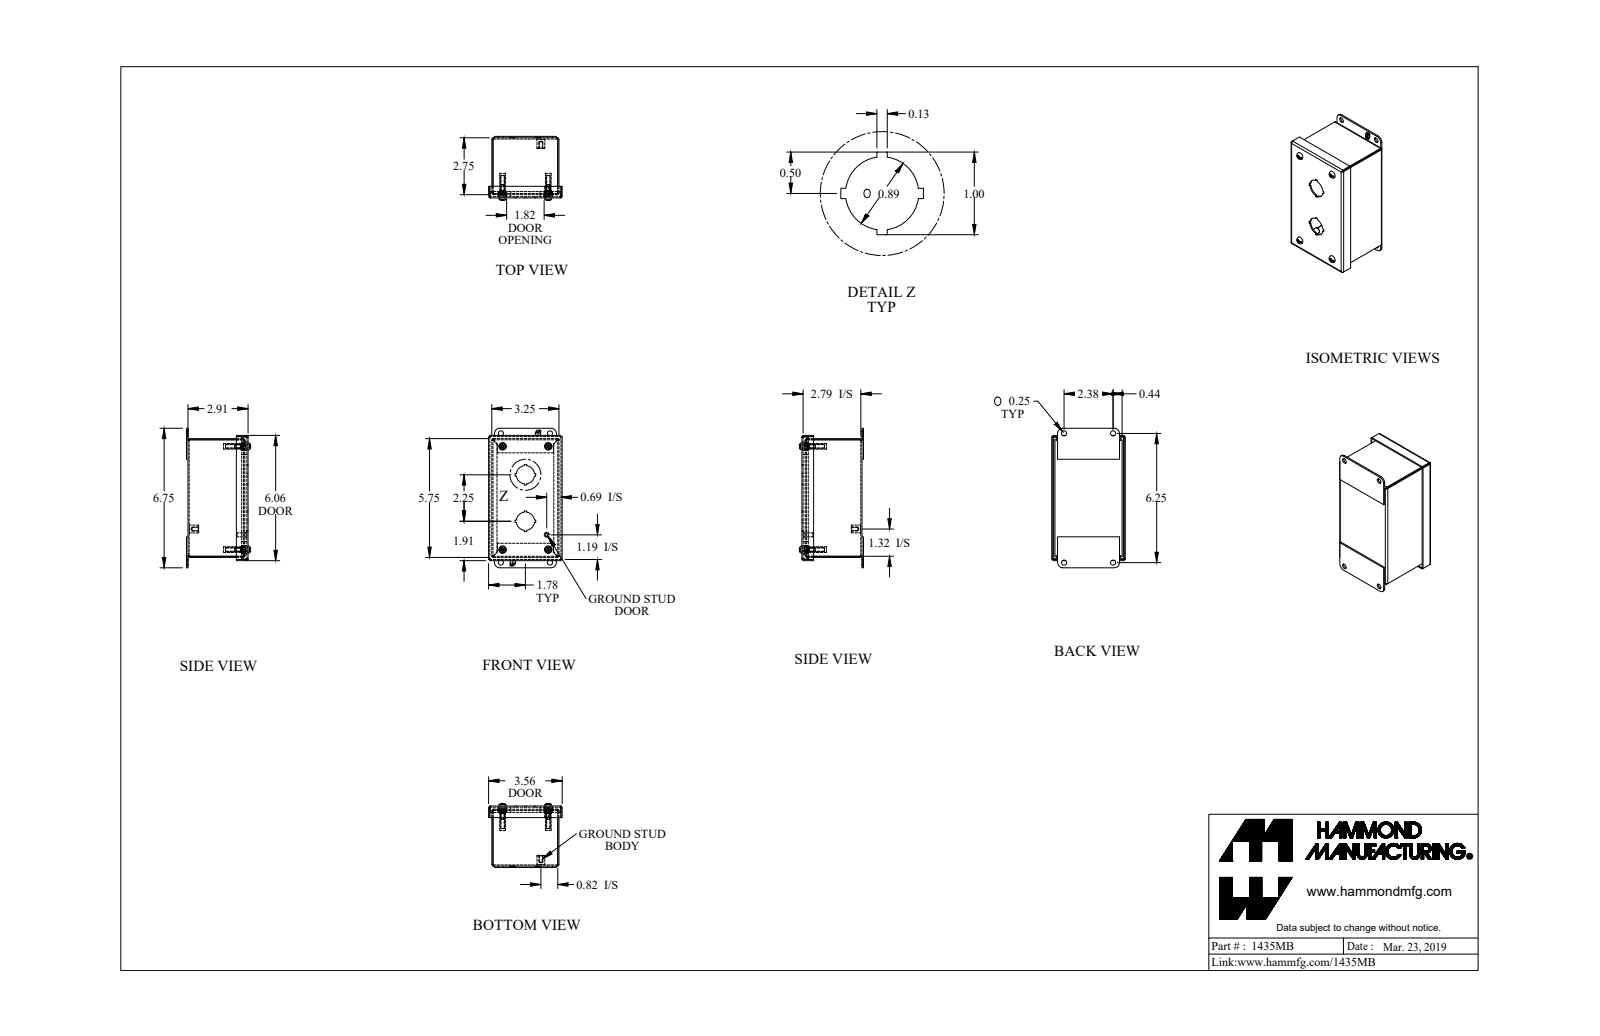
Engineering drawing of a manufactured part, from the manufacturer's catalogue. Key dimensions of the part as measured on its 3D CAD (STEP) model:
Part name (STEP PRODUCT): 1435MB_Default
STEP written by: SolidWorks 2019 (CONFIG_CONTROL_DESIGN)
Units: inches
Bodies: 19 solids, 587 faces (383 planar, 148 cylindrical, 56 other)
Overall size (bounding box): 6.75 × 3.562 × 3.106
Volume: 8.359 in³ · Surface area: 257.5 in²
Round holes (diameter × count): ⌀0.25 ×8, ⌀0.159 ×4, ⌀0.406 ×4, ⌀0.886 ×2, ⌀0.156 ×1
Round bosses / shafts (diameter × count): ⌀0.39 ×4, ⌀0.19 ×4, ⌀0.148 ×4, ⌀0.275 ×2, ⌀0.275 ×2, ⌀0.375 ×1, ⌀0.25 ×1, ⌀0.188 ×1
Partial cylindrical surfaces — rounded edges, fillets, slot ends (radius × count): R0.029 ×12, R0.086 ×12, R0.16 ×4, R0.171 ×4, R0.25 ×4
Main face-to-face distances: 0.057, 2.85, 0.057, 3.193, 2.907, 2.793, 5.693, 3.136, 3.25, 0.156
Hole centre spacings: 5, 2.376, 0.63, 0.631, 1.765, 2.21, 2.211, 2.377
